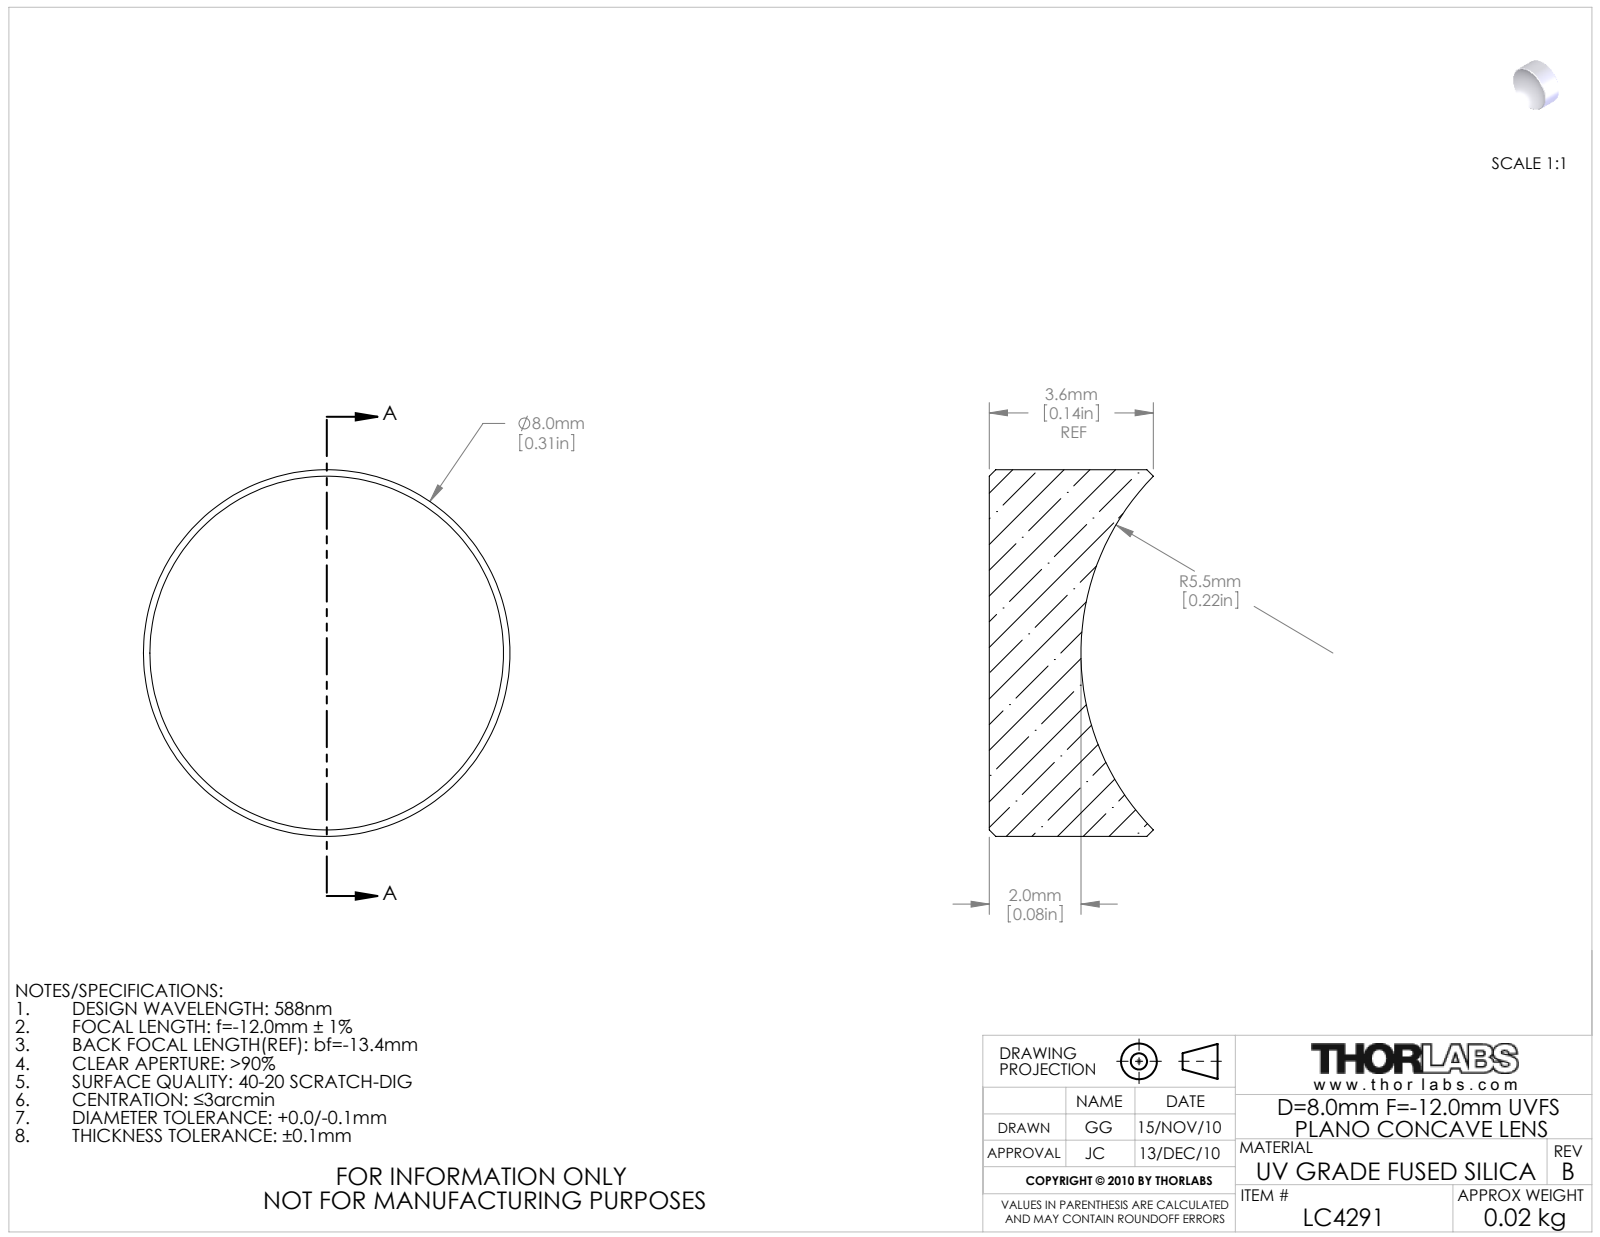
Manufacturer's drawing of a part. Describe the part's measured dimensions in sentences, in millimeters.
The part is named "3493-E0W". Its 3-D file was written by "SolidWorks 2009 (AUTOMOTIVE_DESIGN)". It is 1 solid with 9 faces: 1 planar, 2 cylindrical and 6 other. Overall it measures 8 by 8 by 3.58 millimeters. Its volume is 140 cubic millimeters and its surface area 194 square millimeters. Round bosses or shafts: 1 of diameter 8.
